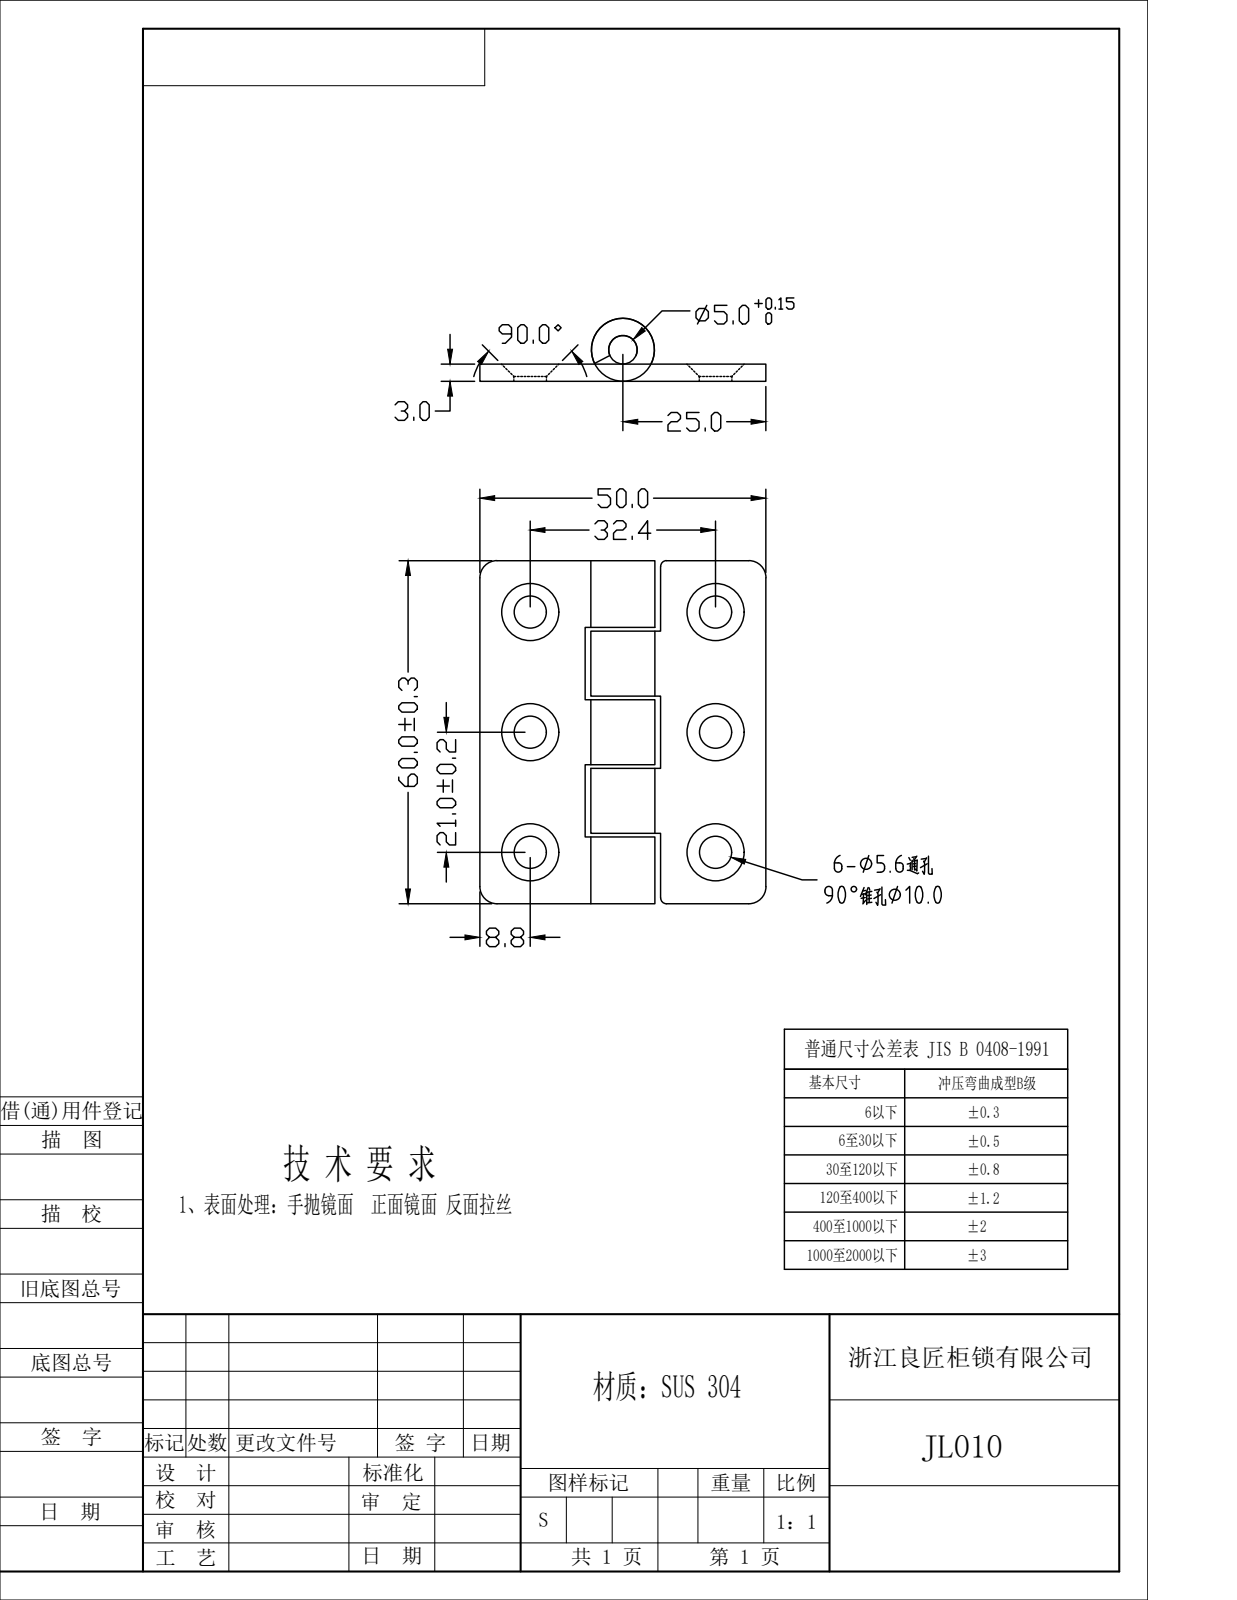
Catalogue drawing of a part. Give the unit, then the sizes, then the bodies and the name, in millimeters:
Units: millimetres
Overall size (bounding box): 60 × 50 × 11
Round holes (diameter × count): ⌀5.6 ×6, ⌀5 ×1
Round bosses / shafts (diameter × count): ⌀11 ×1, ⌀4.7 ×1
Partial cylindrical surfaces — rounded edges, fillets, slot ends (radius × count): R3 ×6
Main face-to-face distances: 3, 12, 0.65, 24, 12.65, 11.35, 60, 24.65, 36, 23.35
Hole centre spacings: 21, 39.96, 34, 42, 54.04
Volume: 5 735 mm³ · Surface area: 9 996 mm²
Bodies: 2 solids, 86 faces (44 planar, 30 cylindrical, 12 other)
STEP written by: Rhino 8.5 (CONFIG_CONTROL_DESIGN)
